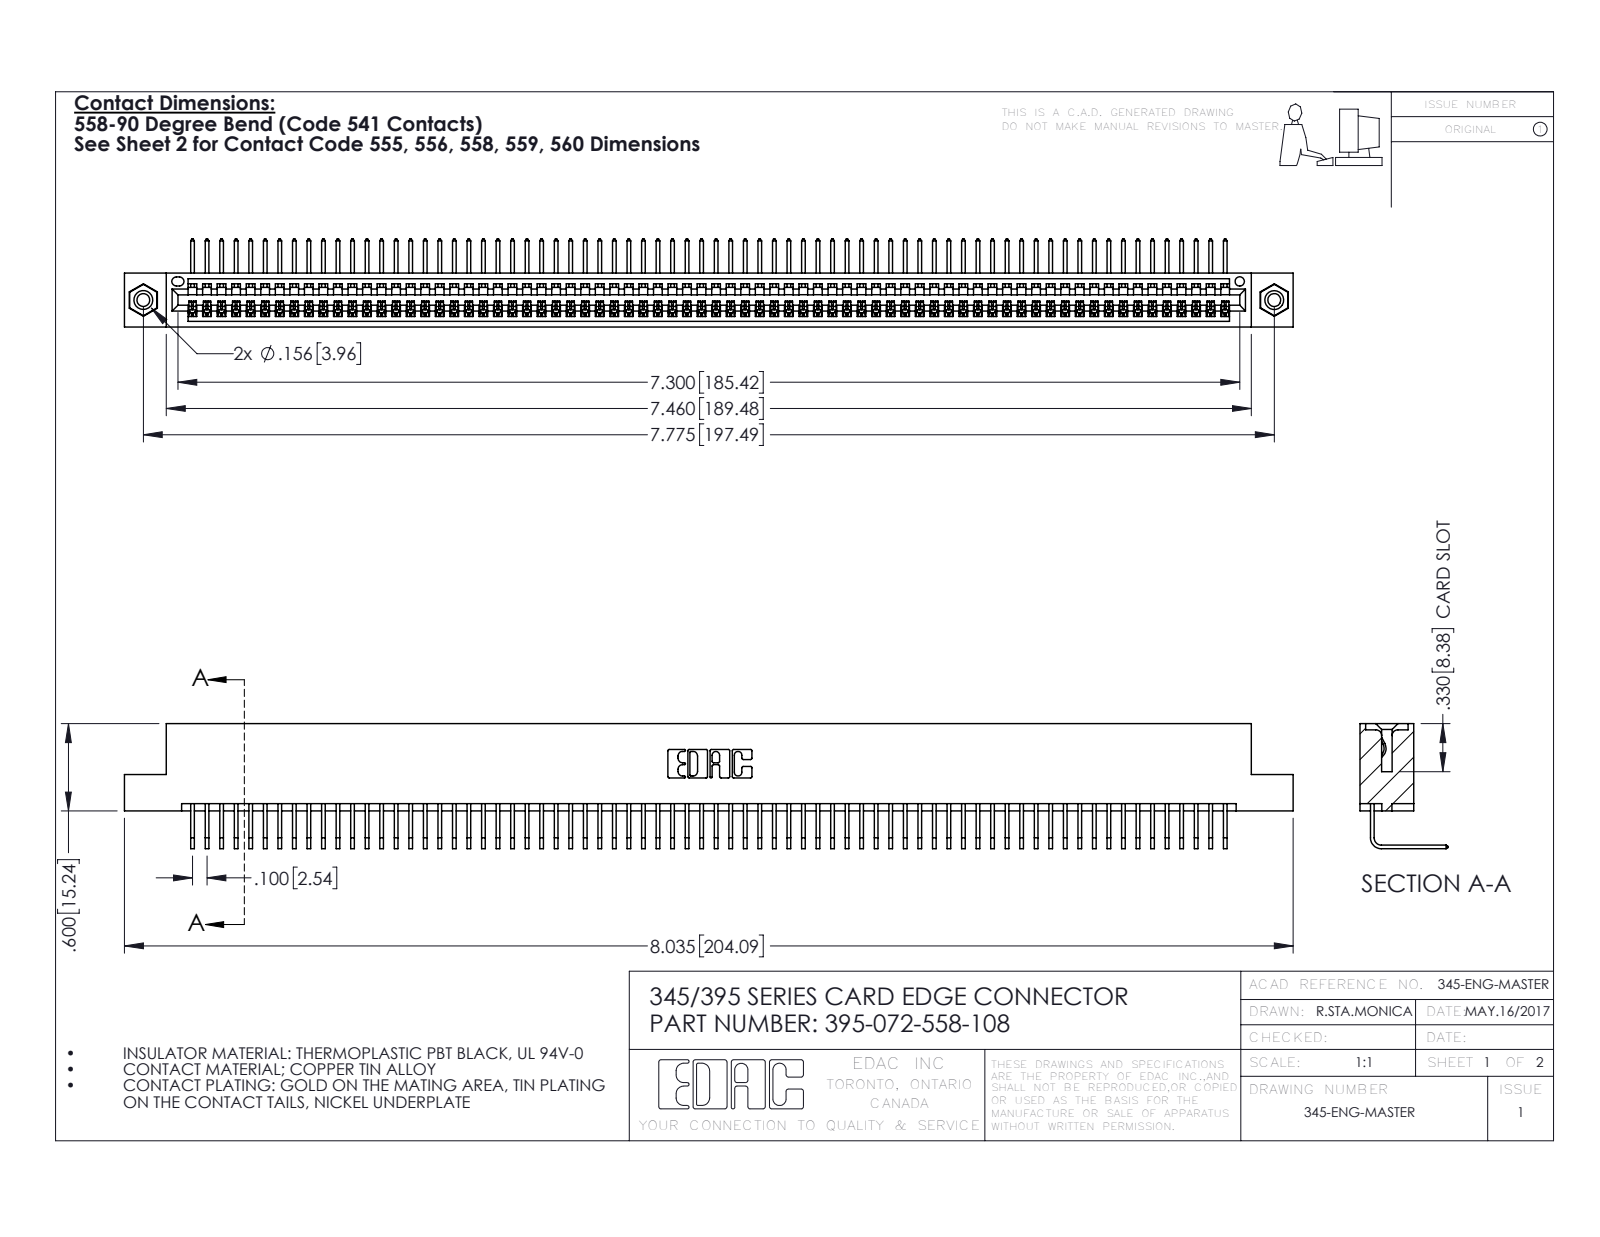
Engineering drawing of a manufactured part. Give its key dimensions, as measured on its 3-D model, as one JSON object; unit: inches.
{"part_name": "345 Part_Flush Mounting Lugs - 0.156 Dia-TI; 345-250-001_345-250-003-102; 395-072-558-108; 345-292-001_558 Tail - 2", "step_written_by": "SolidWorks 2016 (CONFIG_CONTROL_DESIGN)", "units": "inches", "bodies": {"solids": 75, "faces": 4506, "planar": 3136, "cylindrical": 1354, "other": 16}, "overall_size": [8.035, 0.859, 0.605], "volume_in3": 1.212, "surface_area_in2": 43.76, "round_holes": [[0.089, 2], [0.125, 2], [0.156, 2], [0.064, 1]], "round_bosses_or_shafts": [[0.155, 2]], "partial_cylinders_radius": [[0.006, 144], [0.01, 22], [0.007, 6], [0.031, 6], [0.026, 3], [0.031, 2], [0.04, 2], [0.014, 1]], "face_to_face_distances": [0.072, 0.298, 0.37, 0.2, 0.098, 0.272, 0.025, 0.225, 0.149, 0.072], "hole_center_spacings": [0.27, 7.539, 7.775]}
